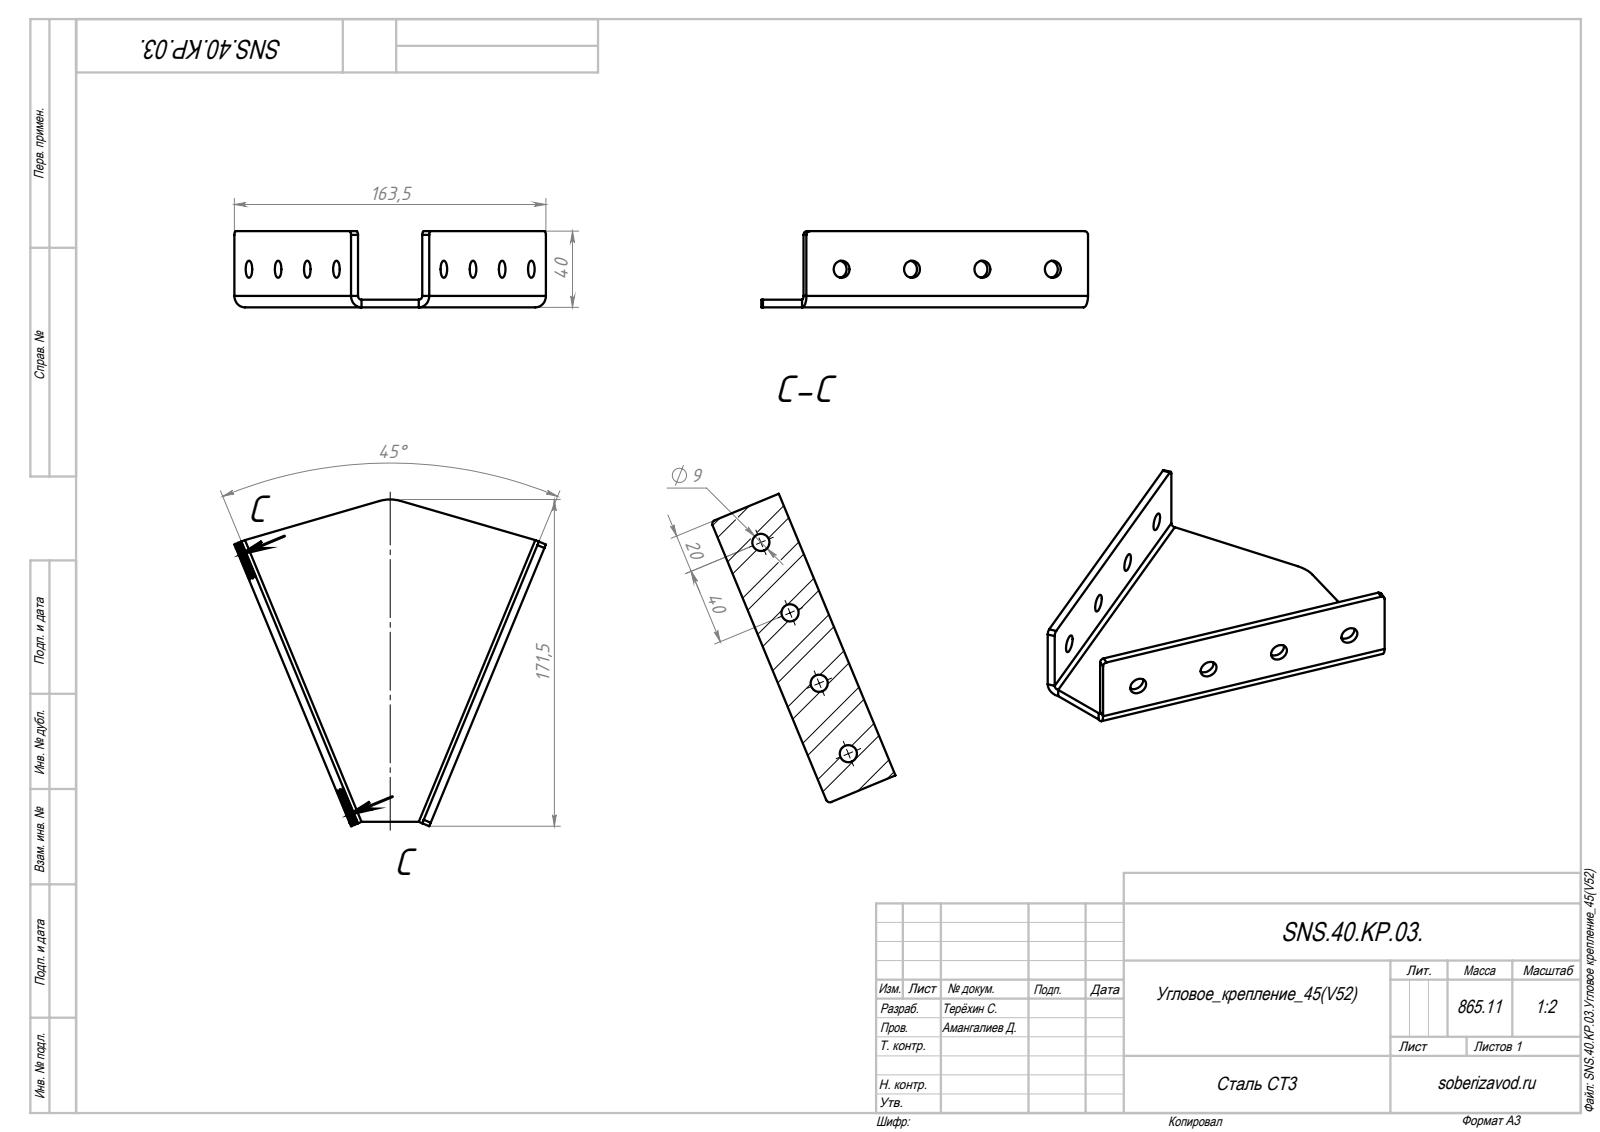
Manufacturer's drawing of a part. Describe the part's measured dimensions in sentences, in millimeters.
Its 3-D file was written by "SolidWorks 2018 (AUTOMOTIVE_DESIGN)". It is 1 solid with 47 faces: 22 planar, 25 cylindrical and 0 other. Overall it measures 171.47 by 163.54 by 40 millimeters. Its volume is 110 204 cubic millimeters and its surface area 58 672 square millimeters. Round holes: 8 of diameter 9. Partial cylindrical surfaces (rounded edges, fillets, slot ends): 6 of radius 2, 2 of radius 6, 1 of radius 20. The main face-to-face distances are 4, 40, 36, 160.03, 160.04. The hole center spacings are 40, 80, 40.01, 80.01, 119.99, 120.01.
